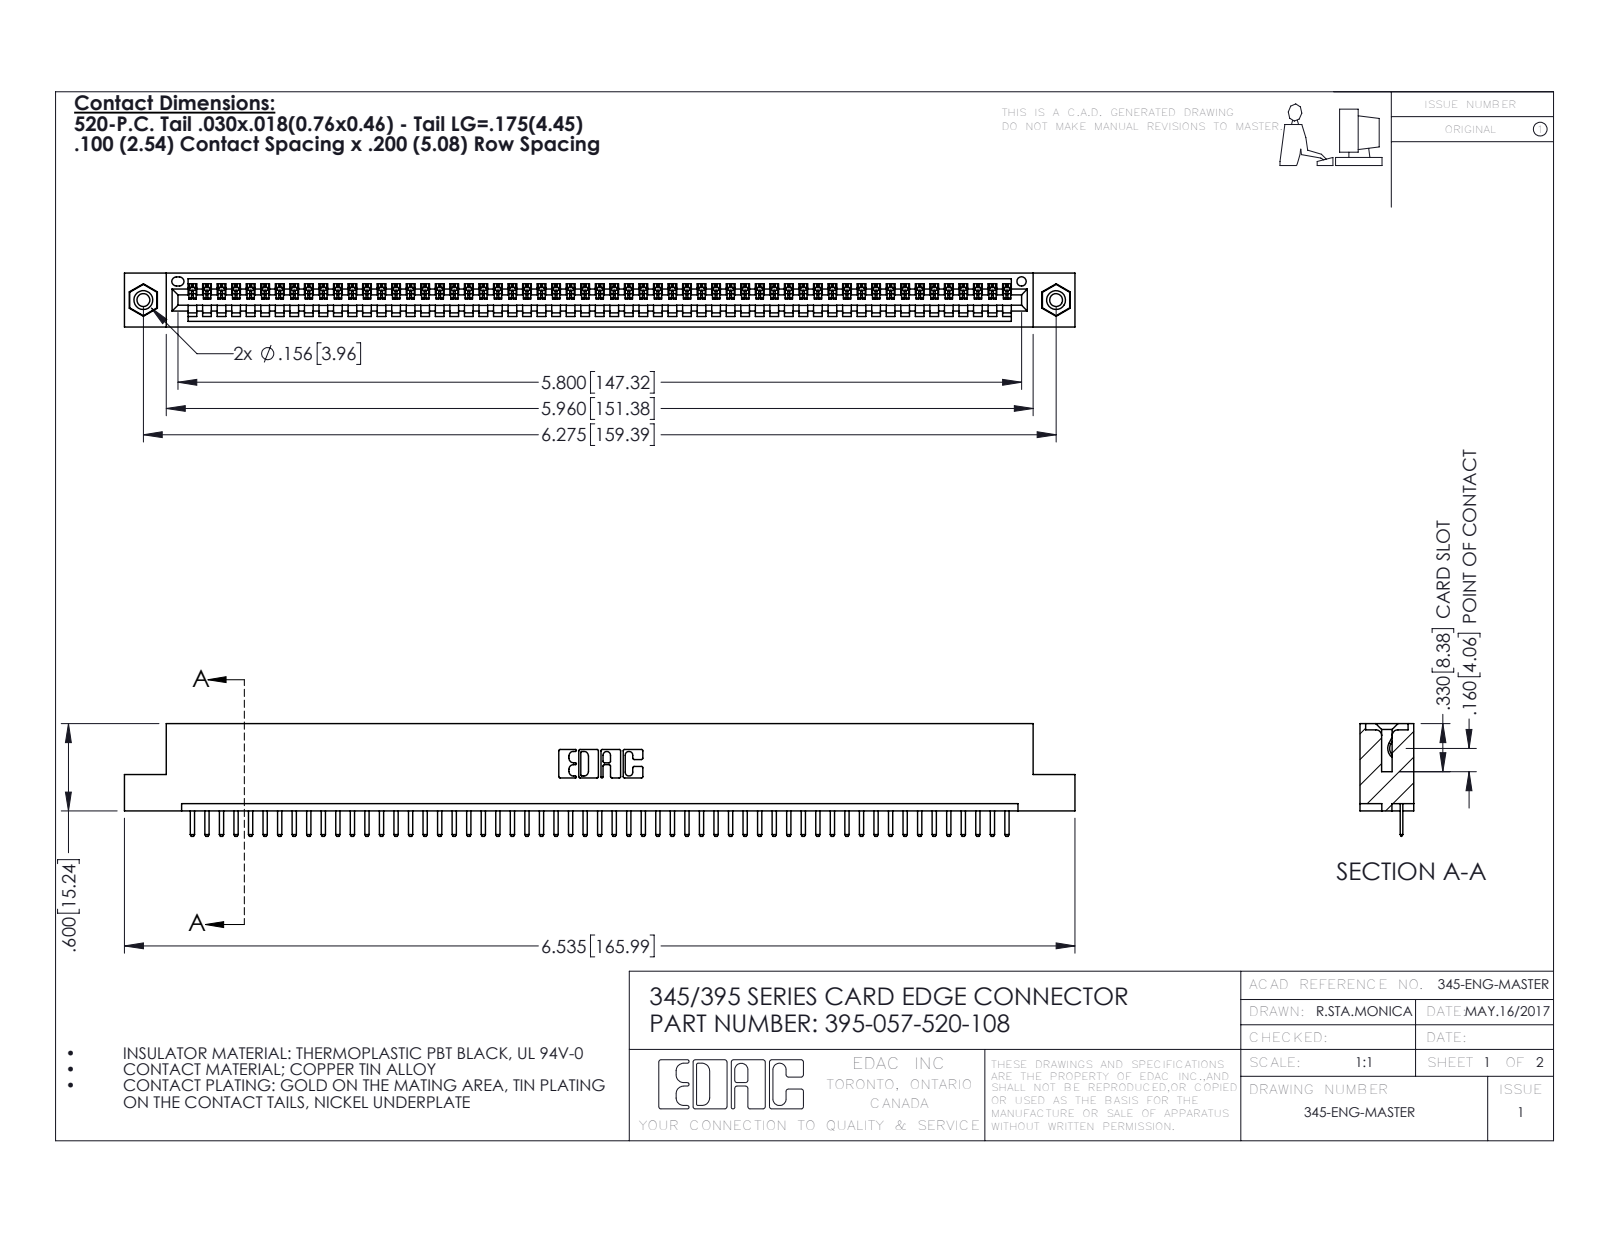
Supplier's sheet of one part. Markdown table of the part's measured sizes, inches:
| quantity | value |
| --- | --- |
| part name | 345-292-001_345-293-120; 345 Part_Flush Mounting Lugs - 0.156 Dia-TI; 345-250-001_345-250-003-102; 395-057-520-108 |
| STEP written by | SolidWorks 2016 (CONFIG_CONTROL_DESIGN) |
| units | inches |
| bodies | 60 solids, 3720 faces (2506 planar, 1198 cylindrical, 16 other) |
| overall size | 6.535 × 0.775 × 0.37 |
| volume | 0.959 in³ |
| surface area | 31.89 in² |
| round holes (diameter × count) | 0.089 × 2, 0.125 × 2, 0.156 × 2, 0.064 × 1 |
| round bosses / shafts (diameter × count) | 0.155 × 2 |
| partial cylindrical surfaces (radius × count) | 0.01 × 116, 0.006 × 114, 0.01 × 22, 0.007 × 6, 0.031 × 6, 0.026 × 3, 0.031 × 2, 0.04 × 2 |
| main face-to-face distances | 0.072, 0.298, 0.37, 0.2, 0.098, 0.272, 0.025, 0.225, 0.072, 0.149 |
| hole center spacings | 0.27, 6.039, 6.275 |
